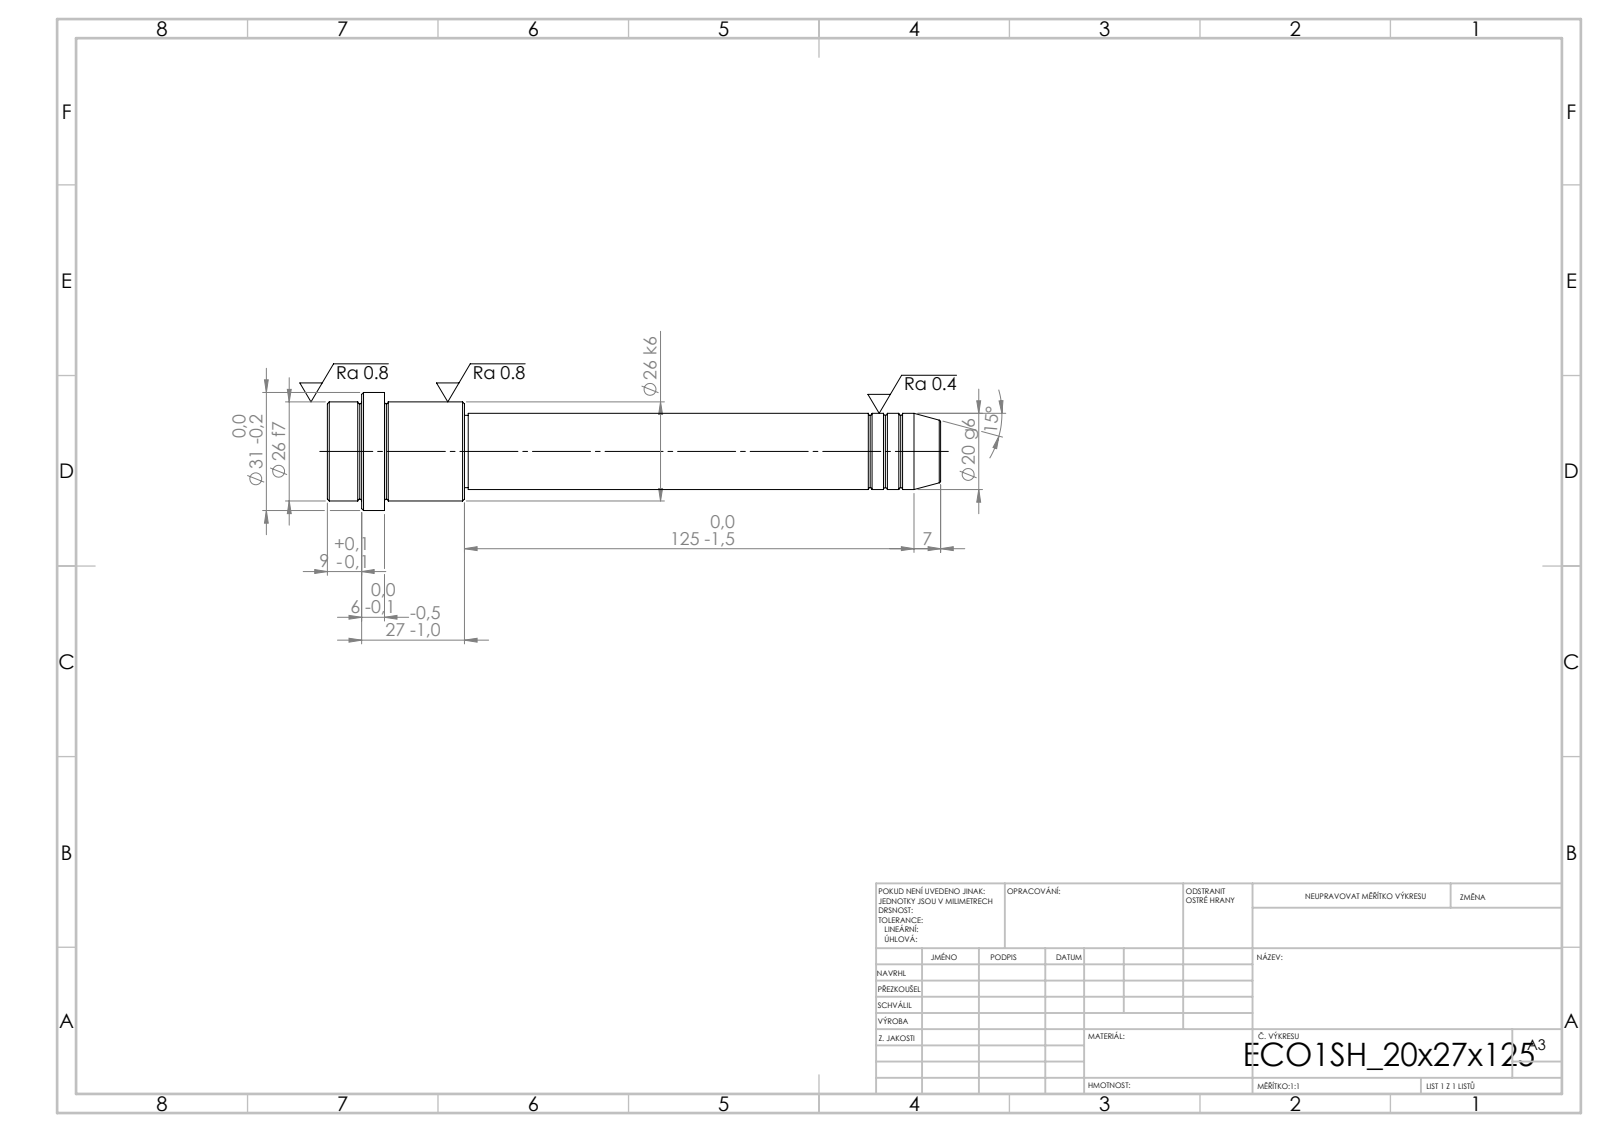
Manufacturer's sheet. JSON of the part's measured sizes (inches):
{"step_written_by": "SolidWorks 2019 (CONFIG_CONTROL_DESIGN)", "units": "inches", "bodies": {"solids": 1, "faces": 52, "planar": 6, "cylindrical": 16, "other": 30}, "overall_size": [6.339, 1.22, 1.22], "volume_in3": 3.609, "surface_area_in2": 19.26, "round_bosses_or_shafts": [[1.22, 1], [1.024, 1], [0.787, 1], [0.748, 1]], "face_to_face_distances": [0.591, 0.827, 1.417, 4.921, 5.748, 6.339, 5.984, 1.063, 0.236, 0.354]}
